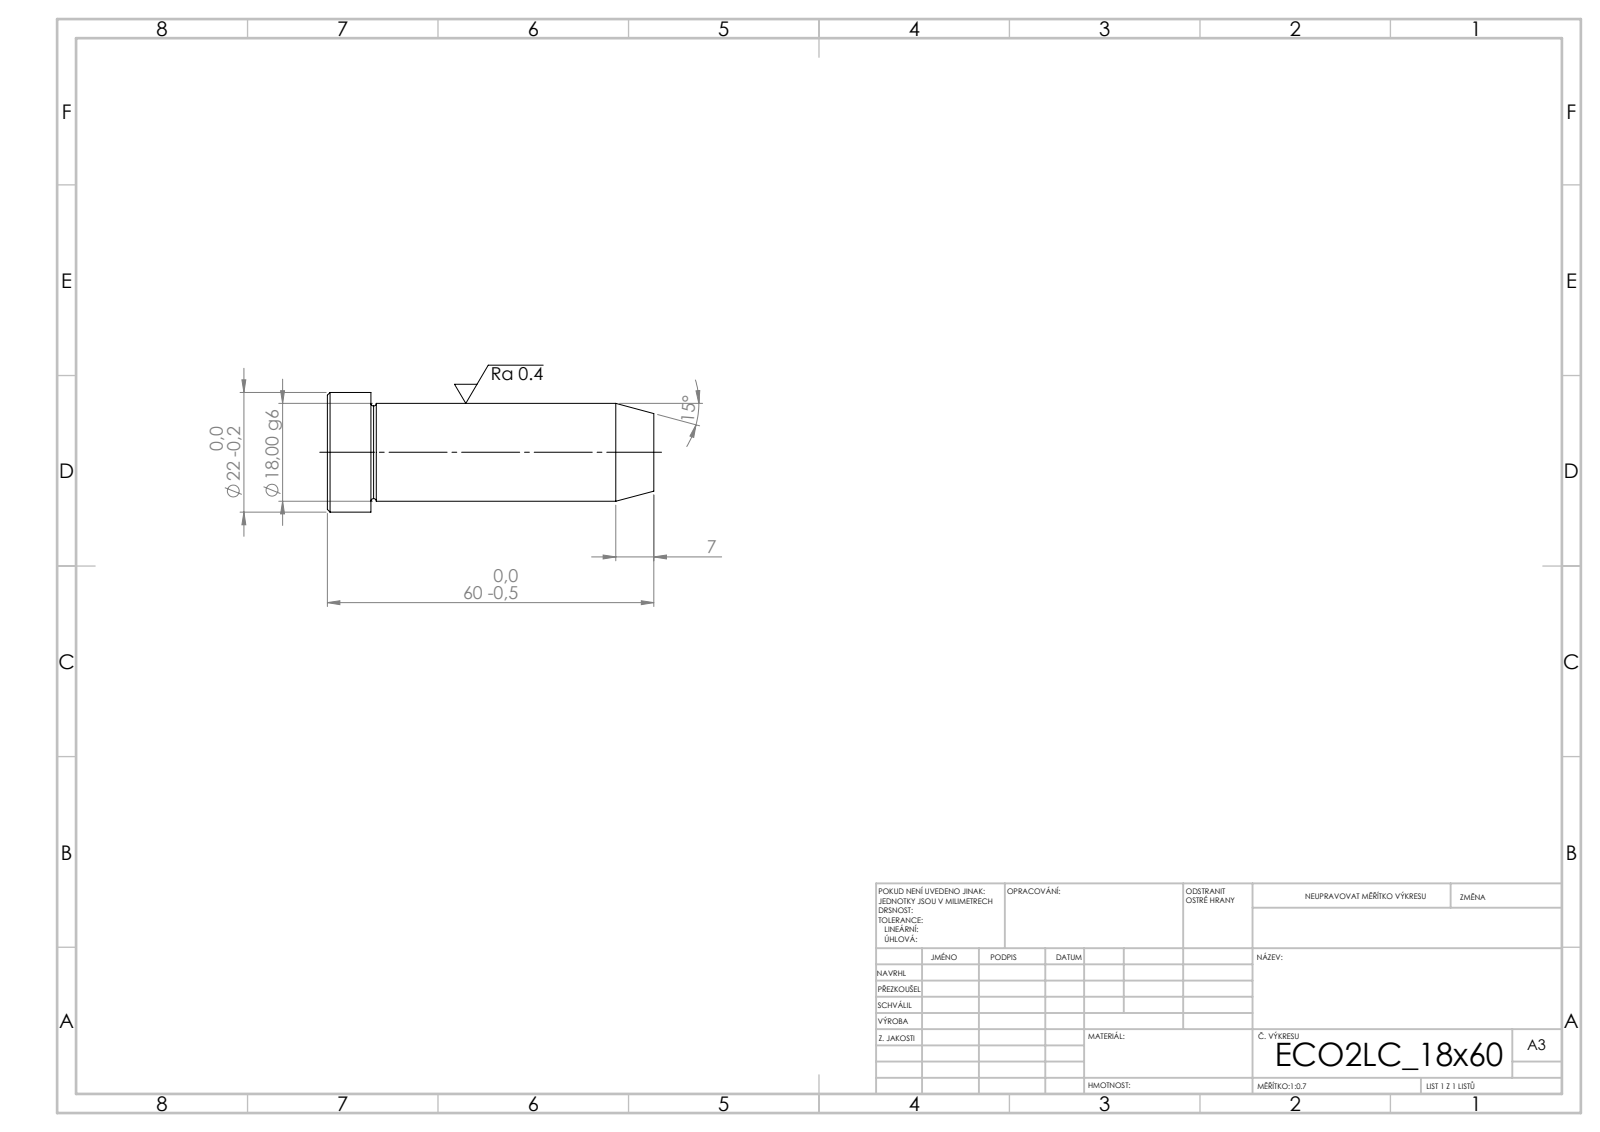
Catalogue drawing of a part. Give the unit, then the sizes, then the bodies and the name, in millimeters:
Units: millimetres
Overall size (bounding box): 60 × 22 × 22
Round bosses / shafts (diameter × count): ⌀22 ×1, ⌀18 ×1
Main face-to-face distances: 60, 52, 8
Volume: 15 898 mm³ · Surface area: 4 139 mm²
Bodies: 1 solid, 15 faces (3 planar, 4 cylindrical, 8 other)
STEP written by: SolidWorks 2019 (CONFIG_CONTROL_DESIGN)
